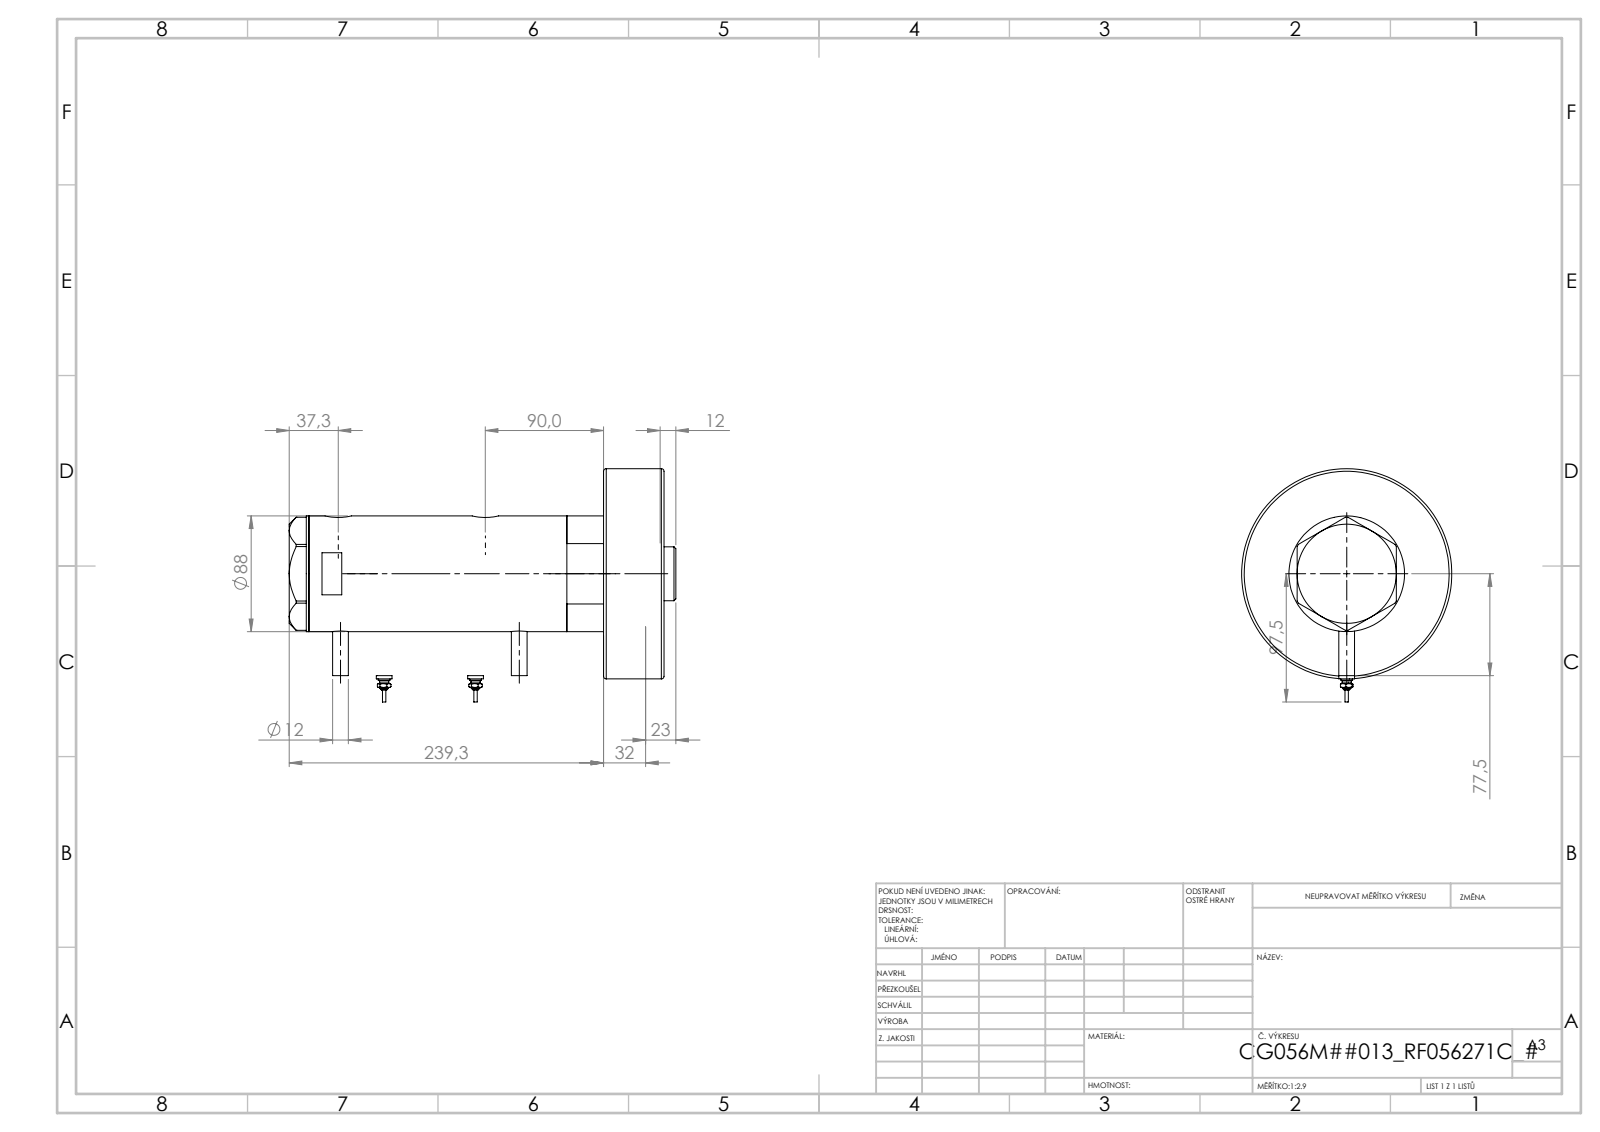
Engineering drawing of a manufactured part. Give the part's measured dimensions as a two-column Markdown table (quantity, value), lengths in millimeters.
| quantity | value |
| --- | --- |
| part name | V270CG_BACK; V270CG_FRONT; V270CG_SWITCH; V270CG_271C (+2 more) |
| STEP written by | SolidWorks 2019 (CONFIG_CONTROL_DESIGN) |
| units | millimeters |
| bodies | 7 solids, 242 faces (83 planar, 81 cylindrical, 78 other) |
| overall size | 237.47 × 160 × 160 |
| volume | 1 951 000 mm³ |
| surface area | 254 274 mm² |
| round holes (diameter × count) | 5 × 2, 12.5 × 2, 13.16 × 2, 20 × 2, 14.5 × 1, 42 × 1, 43.5 × 1, 56 × 1, 60 × 1, 75 × 1, 80 × 1 |
| round bosses / shafts (diameter × count) | 12 × 2, 9 × 2, 7 × 2, 4.34 × 2, 2.4 × 2, 160 × 1, 88 × 1, 73 × 1 |
| main face-to-face distances | 46, 164.9, 210.9, 87.4, 77.5, 123.5, 26, 61.4, 138.9, 184.9 |
| hole center spacings | 1.7, 25.8, 63.3, 65, 89.1, 90.8 |
